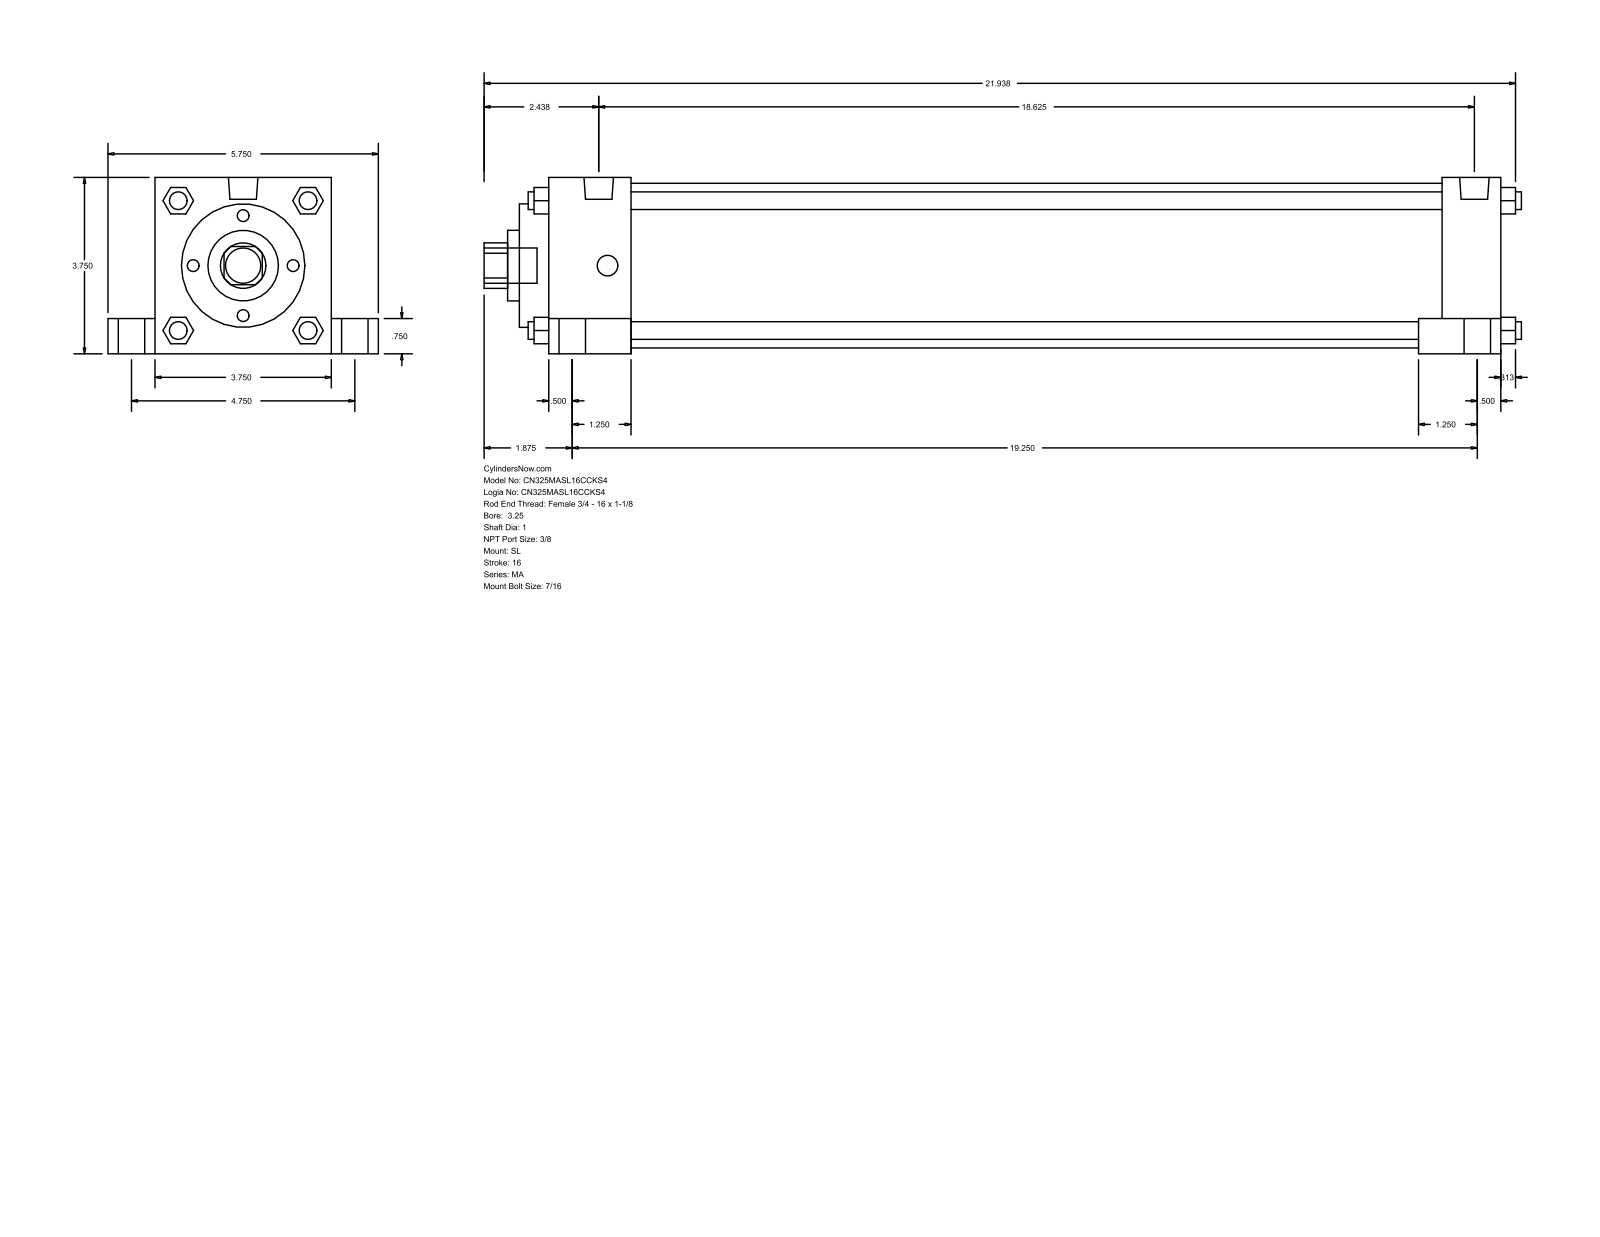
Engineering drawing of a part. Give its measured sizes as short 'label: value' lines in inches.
name: MA_SL__0325_1
written by: GSSL Pune (CONFIG_CONTROL_DESIGN)
unit: in
bodies: 0 solids, 150 faces (113 planar, 37 cylindrical, 0 other)
size: 22.063 × 5.75 × 3.75
holes: 1× ⌀1, 1× ⌀1.5, 1× ⌀2.625, 1× ⌀3.5
bosses: 4× ⌀0.813, 4× ⌀0.563, 4× ⌀0.437, 4× ⌀0.375, 2× ⌀0.627, 1× ⌀0.75
rounds: 1× R0.484
face distances: 3.75, 20.25, 0.625, 1, 4.75, 20.875, 0.75, 19, 1.25, 1.75
